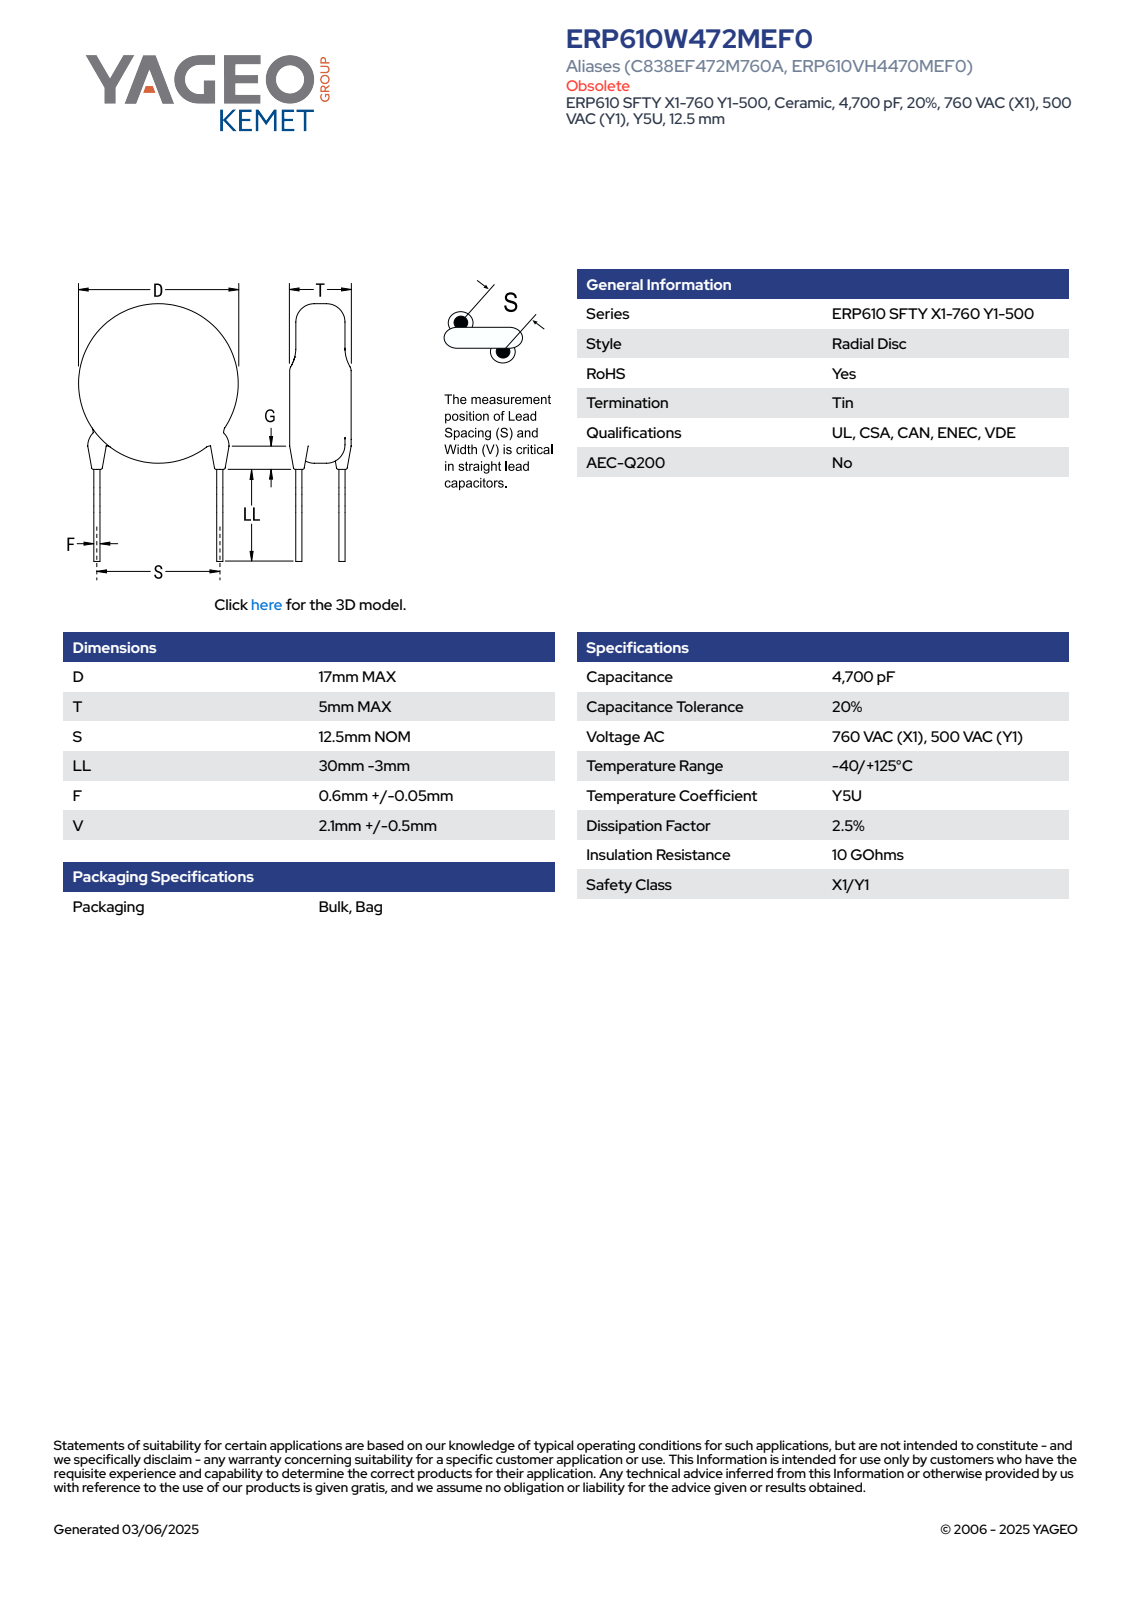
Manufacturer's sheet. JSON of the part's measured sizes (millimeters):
{"part_name": "CCD_KST_17X5_D17T5S12.5LL27F0.65G3V2.6", "step_written_by": "SolidWorks 2014 (AUTOMOTIVE_DESIGN)", "units": "millimeters", "bodies": {"solids": 4, "faces": 81, "planar": 63, "cylindrical": 6, "other": 12}, "overall_size": [44.15, 17, 5], "volume_mm3": 1133, "surface_area_mm2": 823, "round_bosses_or_shafts": [[0.65, 2], [17, 1]], "face_to_face_distances": [5, 36.7, 34.59, 2.11, 0.52, 0.39, 6.27, 6.51, 35, 0.41]}
